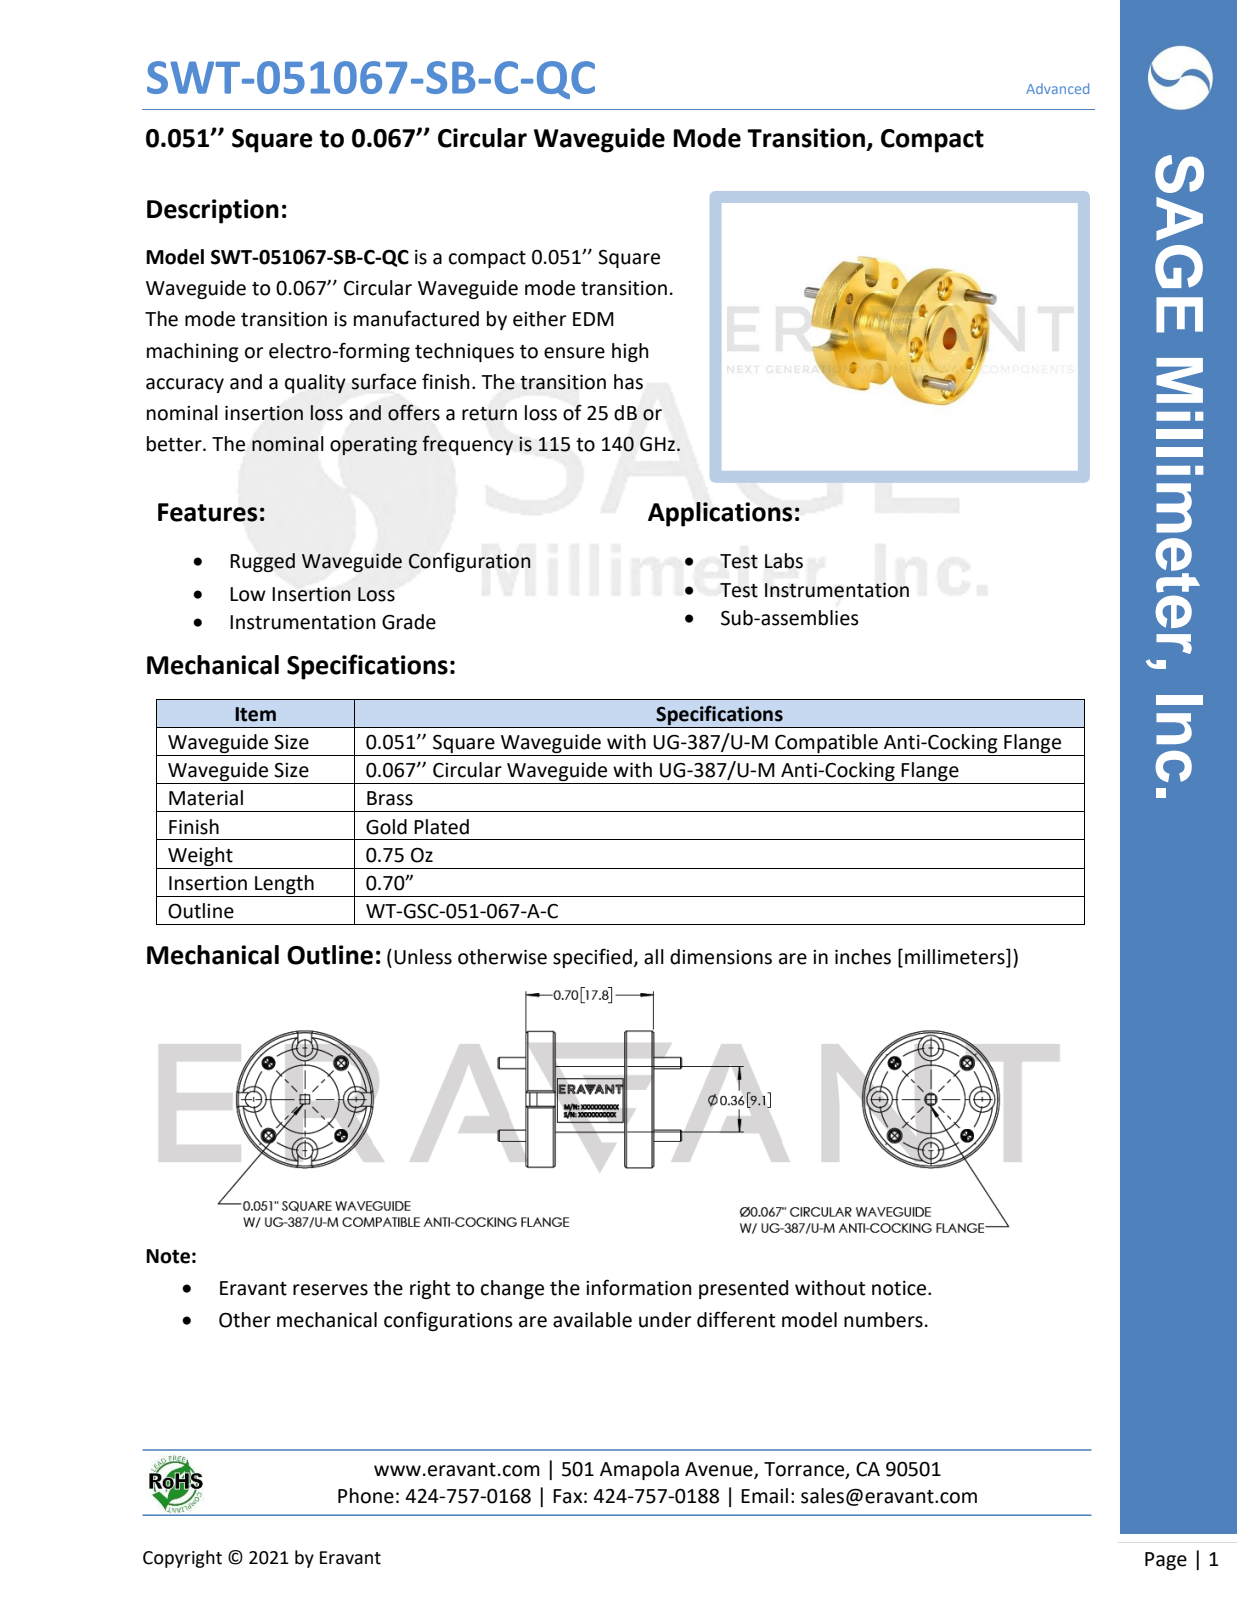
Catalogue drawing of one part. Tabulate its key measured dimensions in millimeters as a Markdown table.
| quantity | value |
| --- | --- |
| part name | SWT-051067-SB-C-QC |
| STEP written by | SolidWorks 2021 (CONFIG_CONTROL_DESIGN) |
| units | millimeters |
| bodies | 5 solids, 175 faces (45 planar, 78 cylindrical, 52 other) |
| overall size | 25.5 × 19.1 × 19.1 |
| volume | 2 570 mm³ |
| surface area | 2 221 mm² |
| round holes (diameter × count) | 1.5 × 4, 1.7 × 4, 2.3 × 4, 3.6 × 4, 17.3 × 1 |
| round bosses / shafts (diameter × count) | 1.6 × 4, 19.1 × 1, 9.5 × 1, 9.1 × 1 |
| main face-to-face distances | 3.6, 13.2, 0.5, 4.1, 13.7, 17.3, 9.7, 16.8, 17.8, 1.5 |
| hole center spacings | 5.5, 7.1, 10.1, 13.2, 14.3 |
